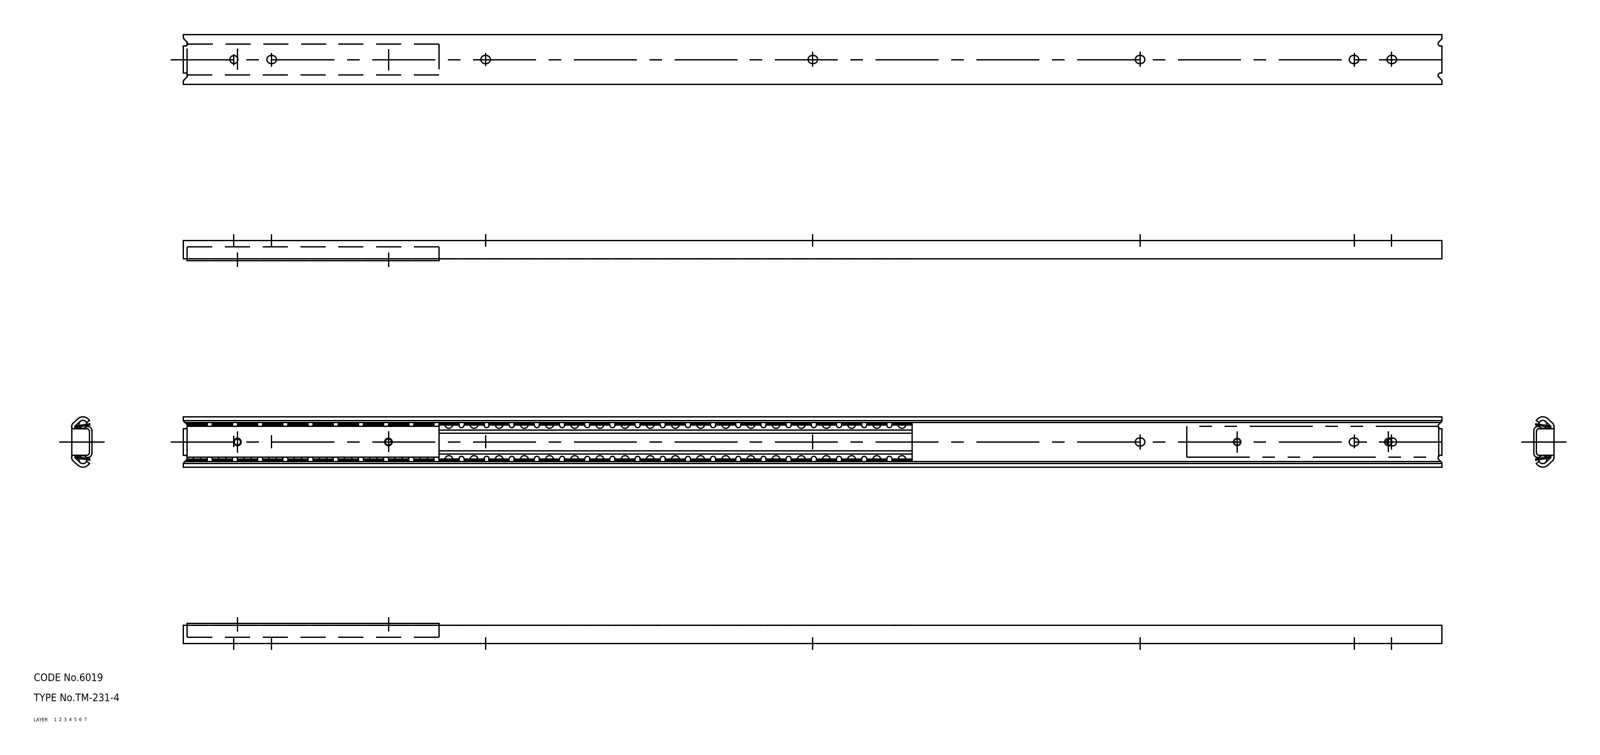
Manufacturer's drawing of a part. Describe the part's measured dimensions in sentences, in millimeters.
The part is named "ball; retainer; member_B; member_A (+1 more)". Its 3-D file was written by "CADfix (AUTOMOTIVE_DESIGN)". It is 61 solids with 744 faces: 0 planar, 0 cylindrical and 744 other. Overall it measures 500 by 20 by 8 millimeters. Its volume is 25 788 cubic millimeters and its surface area 48 725 square millimeters.
